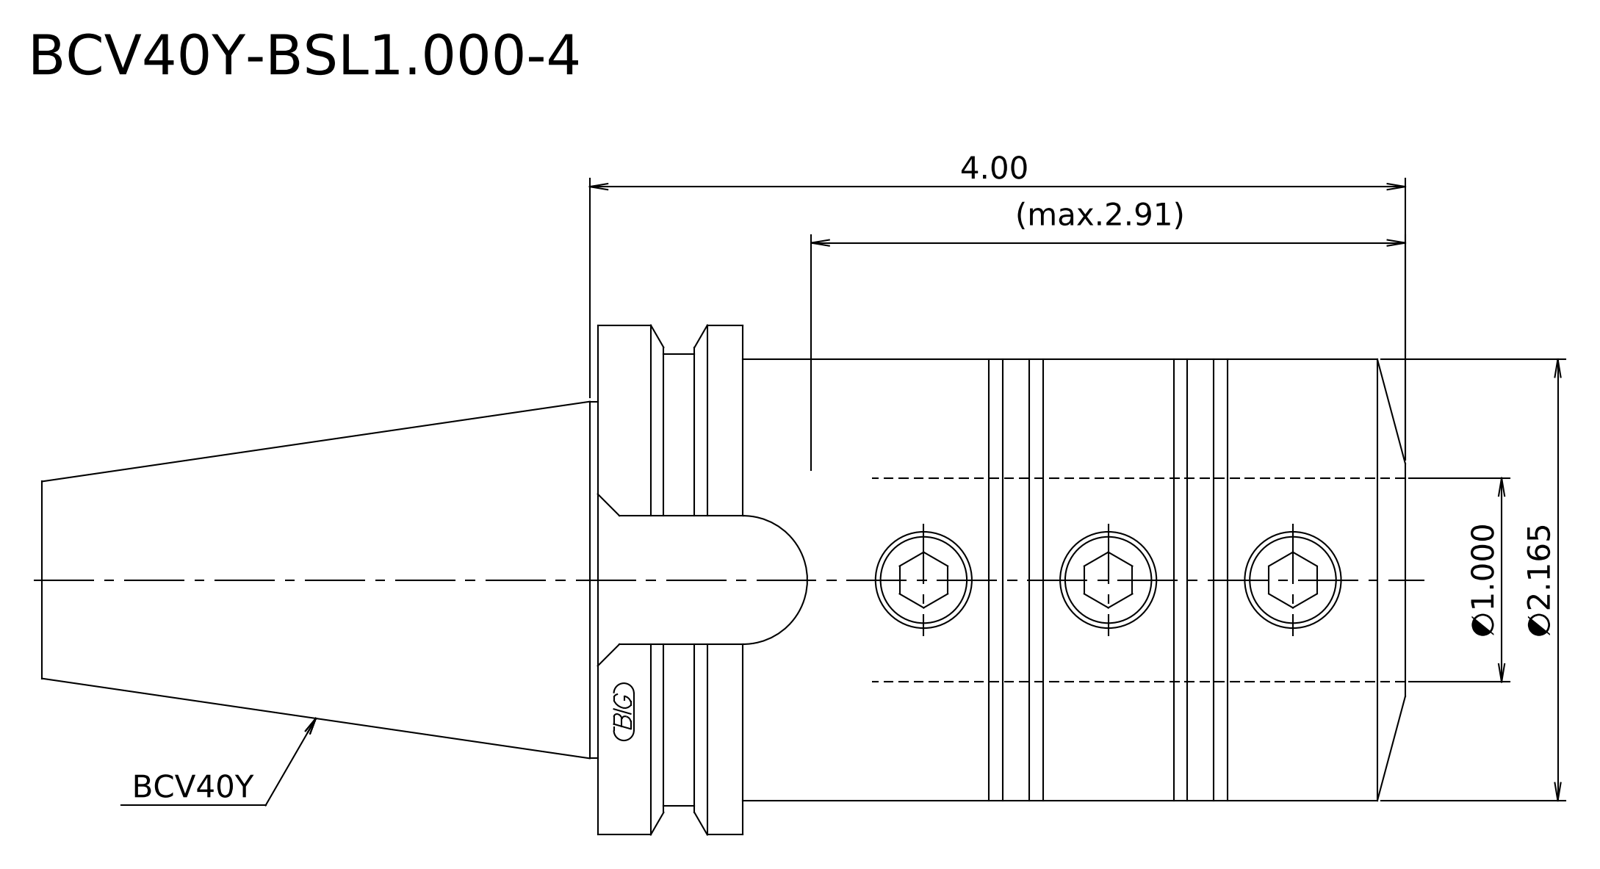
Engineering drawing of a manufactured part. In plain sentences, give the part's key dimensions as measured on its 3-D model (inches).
Its 3-D file was written by "Kubotek KeyCreator 2011 V10.0.2 (22737) (automotive_design)". It is 1 solid with 15 faces: 6 planar, 5 cylindrical and 4 other. Overall it measures 6.687 by 2.5 by 2.5 inches. Its volume is 19.14 cubic inches and its surface area 48.01 square inches. Round bosses or shafts: 1 of diameter 2.5, 1 of diameter 2.219, 1 of diameter 2.165, 1 of diameter 1.75. The main face-to-face distances are 0.711, 3.25, 3.961, 6.687, 3.437, 2.726, 3.638, 0.388, 0.323, 3.049.
